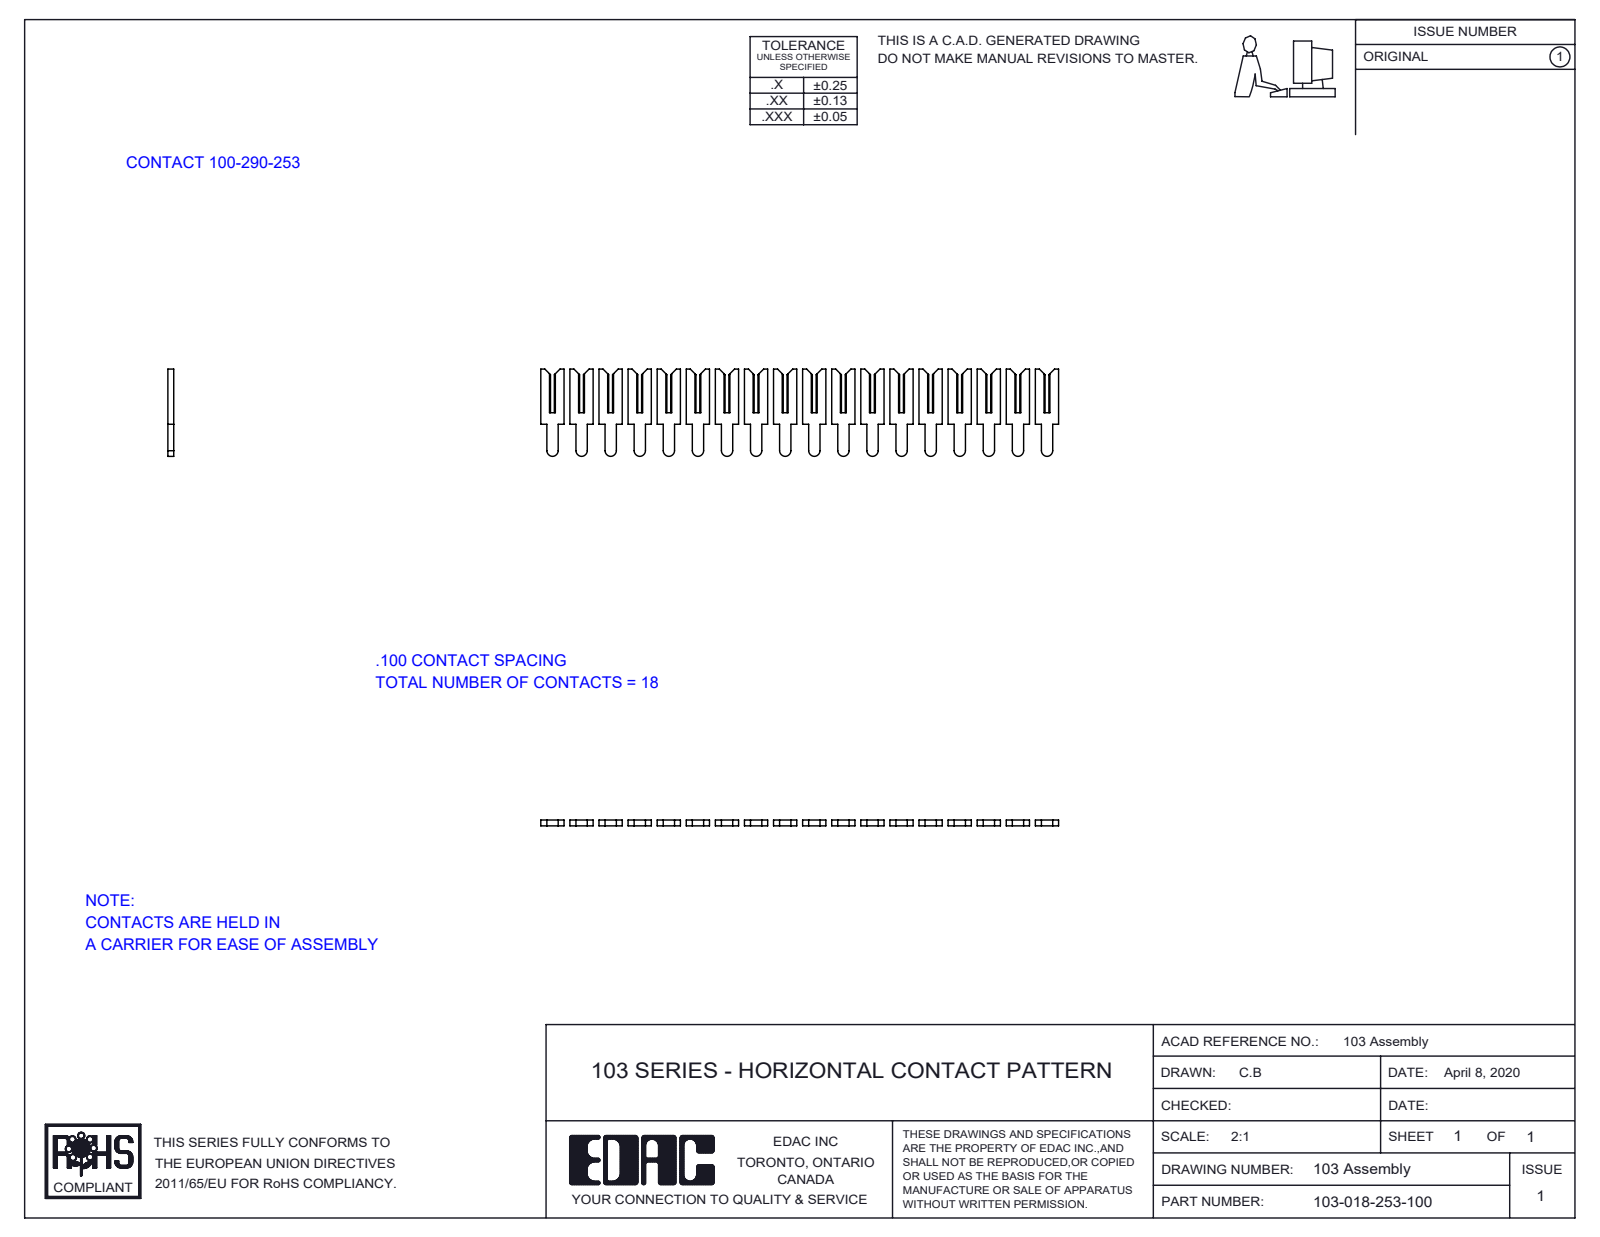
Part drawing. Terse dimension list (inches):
name: 103-018-253-100; 100-290-001_100-290-253
written by: SolidWorks 2016 (CONFIG_CONTROL_DESIGN)
unit: in
bodies: 18 solids, 360 faces (342 planar, 18 cylindrical, 0 other)
size: 1.78 × 0.3 × 0.02
volume: 0.006 in³; area: 0.96 in²
rounds: 18× R0.019
face distances: 0.02, 0.1, 0.2, 0.3, 0.4, 0.5, 0.141, 0.6, 0.354, 0.7
